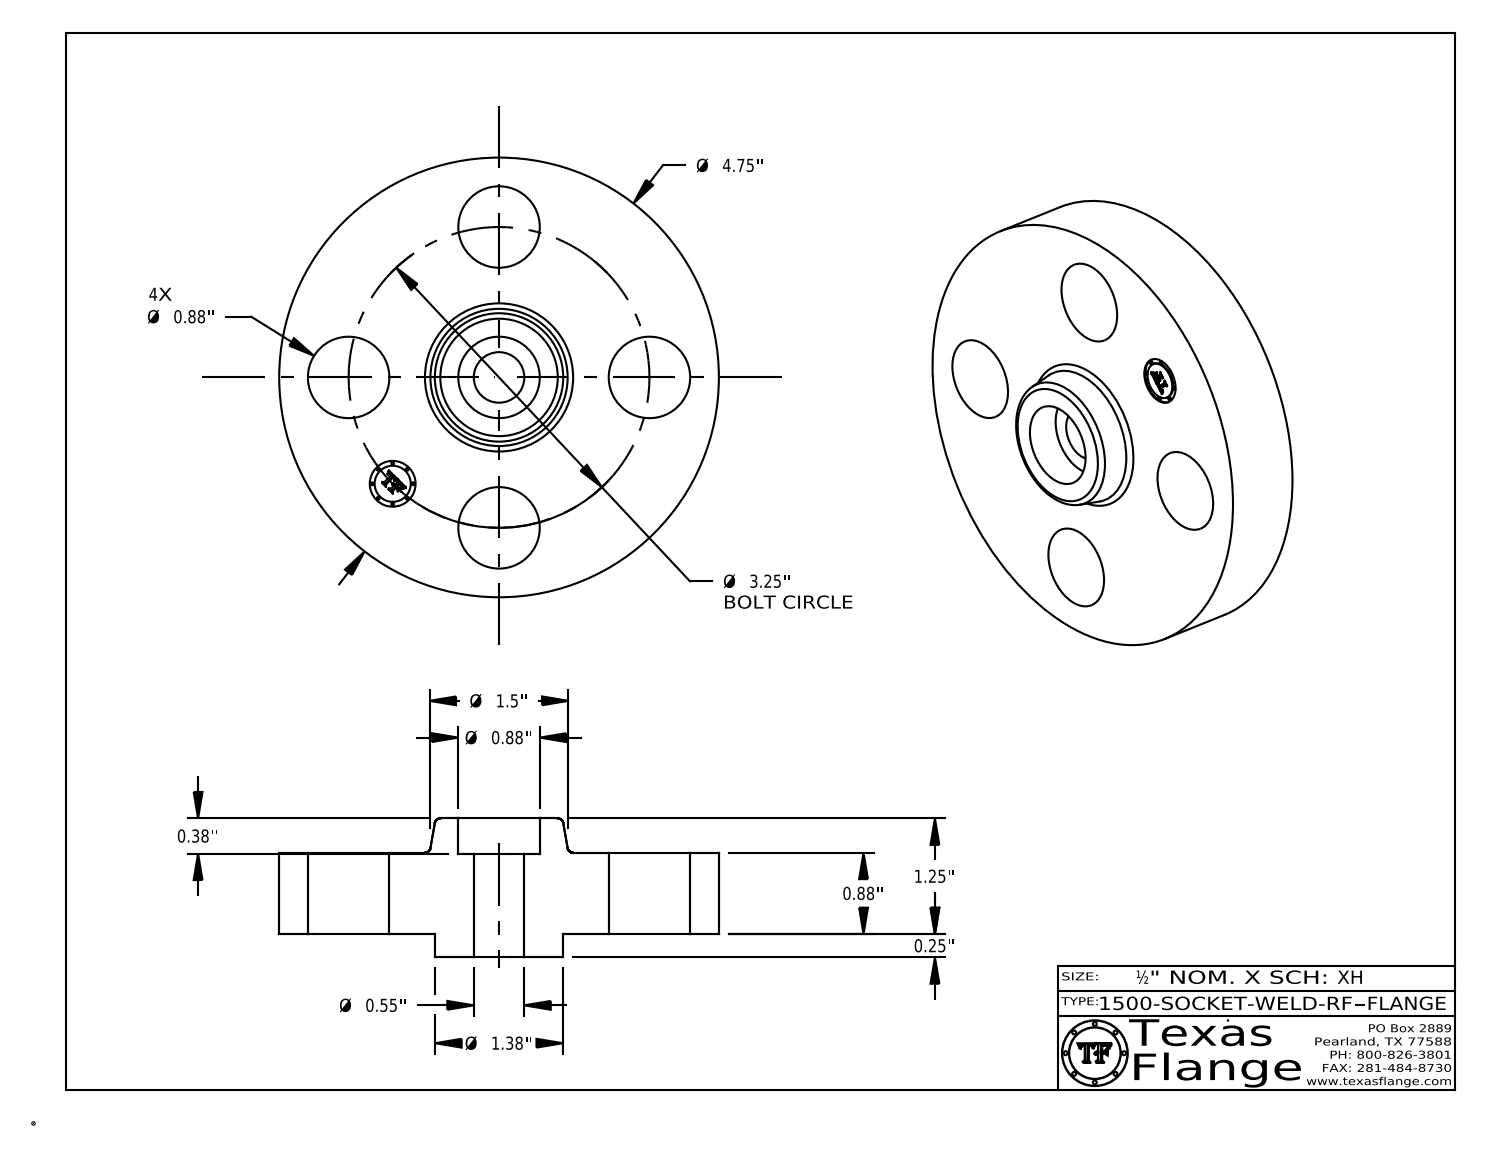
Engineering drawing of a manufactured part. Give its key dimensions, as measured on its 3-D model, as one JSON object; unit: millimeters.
{"part_name": "1500-SOCKET-WELD-RF", "step_written_by": "CATIA V5 STEP AP214 (AUTOMOTIVE_DESIGN)", "units": "millimeters", "bodies": {"solids": 1, "faces": 412, "planar": 370, "cylindrical": 36, "other": 6}, "overall_size": [120.7, 120.7, 38.1], "volume_mm3": 228300, "surface_area_mm2": 37660, "round_holes": [[22.4, 5], [12.6, 1], [13.9, 1]], "round_bosses_or_shafts": [[0.8, 8], [120.7, 1], [35.1, 1], [9.9, 1]], "face_to_face_distances": [22.4, 6.4, 28.7, 38.1, 31.8, 9.4, 28.4, 22.1, 9.7, 28.3], "hole_center_spacings": [41.3, 58.4, 31.6, 76.3, 82.6]}
